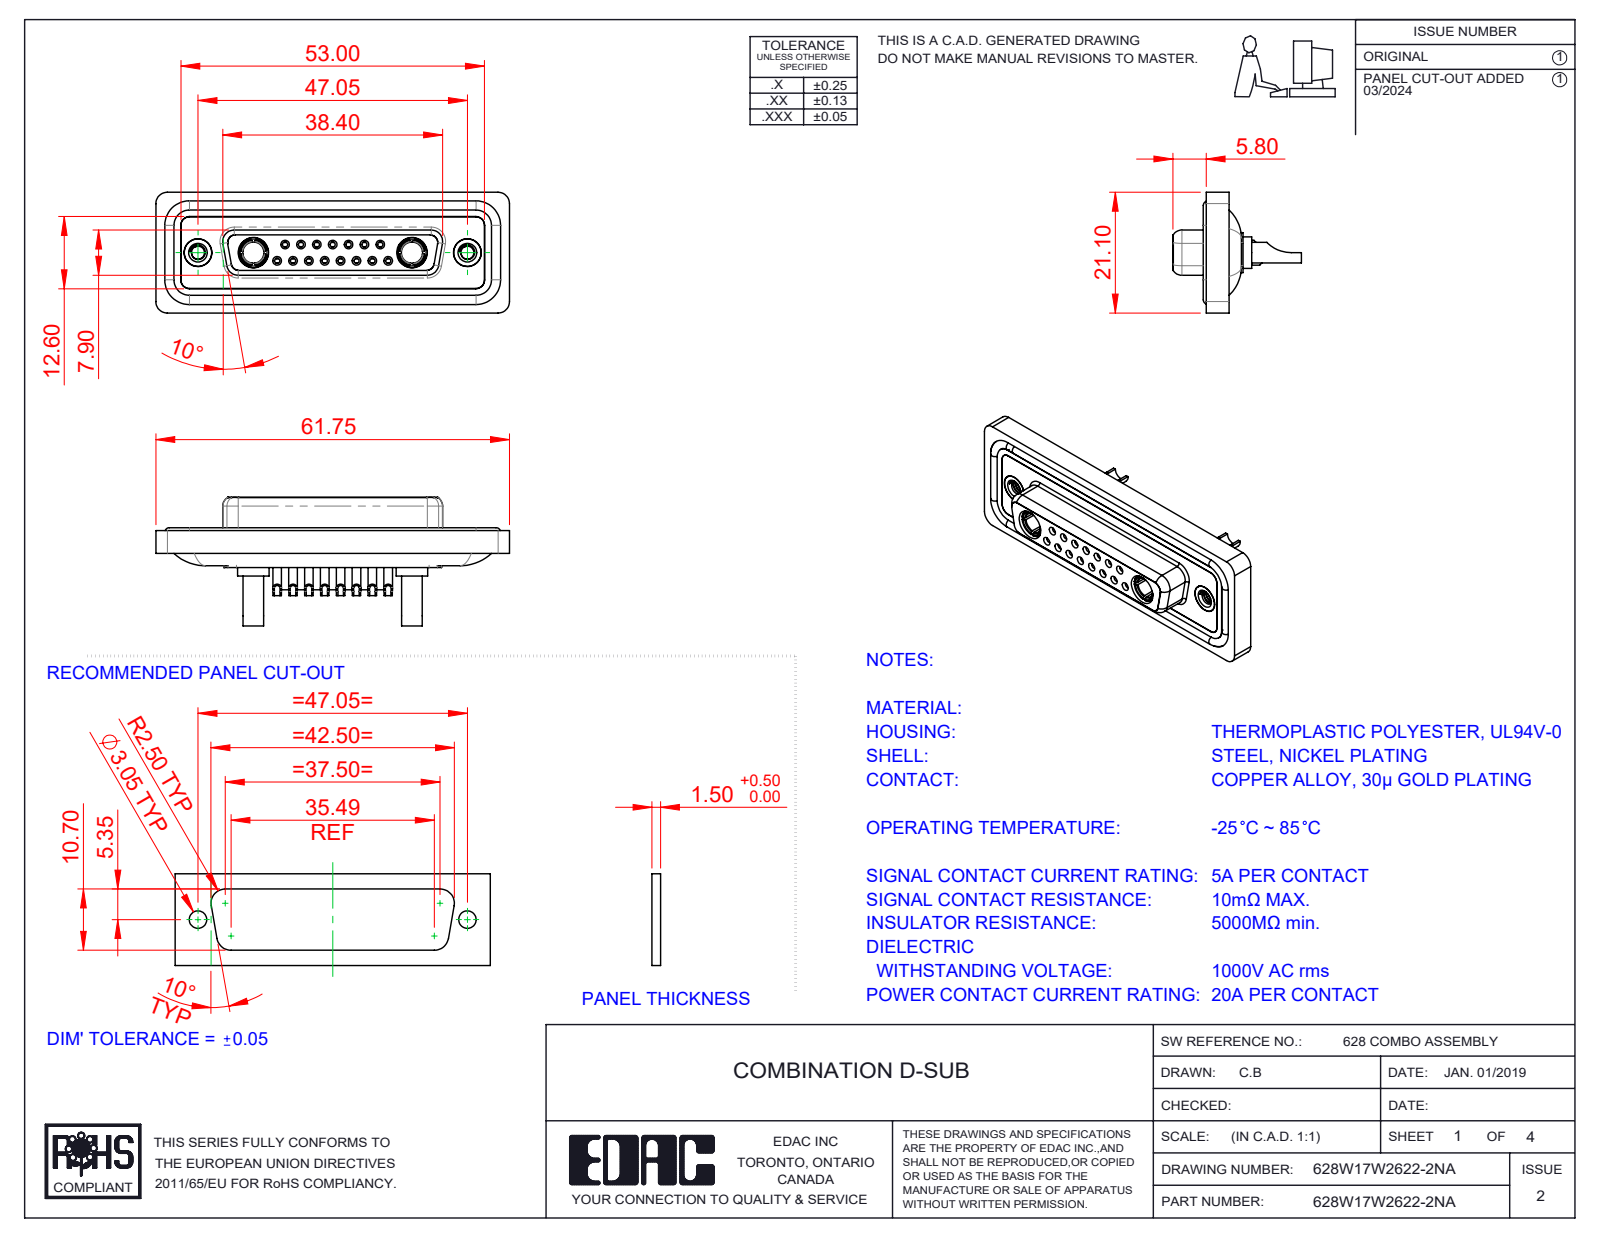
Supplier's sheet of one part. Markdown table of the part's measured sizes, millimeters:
| quantity | value |
| --- | --- |
| part name | 628Combo Threaded Rivet_A; 628Combo Housing_17W2; 628Combo Shell Front_25 Contacts; 628Combo Contact Row 1_22 (+5 more) |
| STEP written by | SolidWorks 2023 (CONFIG_CONTROL_DESIGN) |
| units | millimeters |
| bodies | 26 solids, 1369 faces (424 planar, 557 cylindrical, 388 other) |
| overall size | 61.75 × 22.45 × 21.1 |
| volume | 8 383 mm³ |
| surface area | 14 178 mm² |
| round holes (diameter × count) | 0.9 × 15, 1 × 15, 1.1 × 15, 1.5 × 15, 2 × 15, 1.6 × 8, 1.7 × 7, 4.85 × 4, 2.26 × 2, 2.7 × 2, 3.7 × 2, 4 × 2 |
| round bosses / shafts (diameter × count) | 2.2 × 15, 1.6 × 11, 5.5 × 2, 5.2 × 2, 4.96 × 2, 4.95 × 2, 4.8 × 2, 4.75 × 2 |
| partial cylindrical surfaces (radius × count) | 1.5 × 22, 2 × 18, 1.35 × 8, 1.6 × 8, 1 × 6, 0.25 × 4, 0.5 × 4, 0.6 × 4 |
| main face-to-face distances | 0.4, 1.8, 7.45, 5.65, 6.6, 0.5, 7.05, 1.6, 2.9, 1.1 |
| hole center spacings | 3.16, 2.77, 8.31, 5.54, 5.03, 5.04, 7.49, 11.08 |
